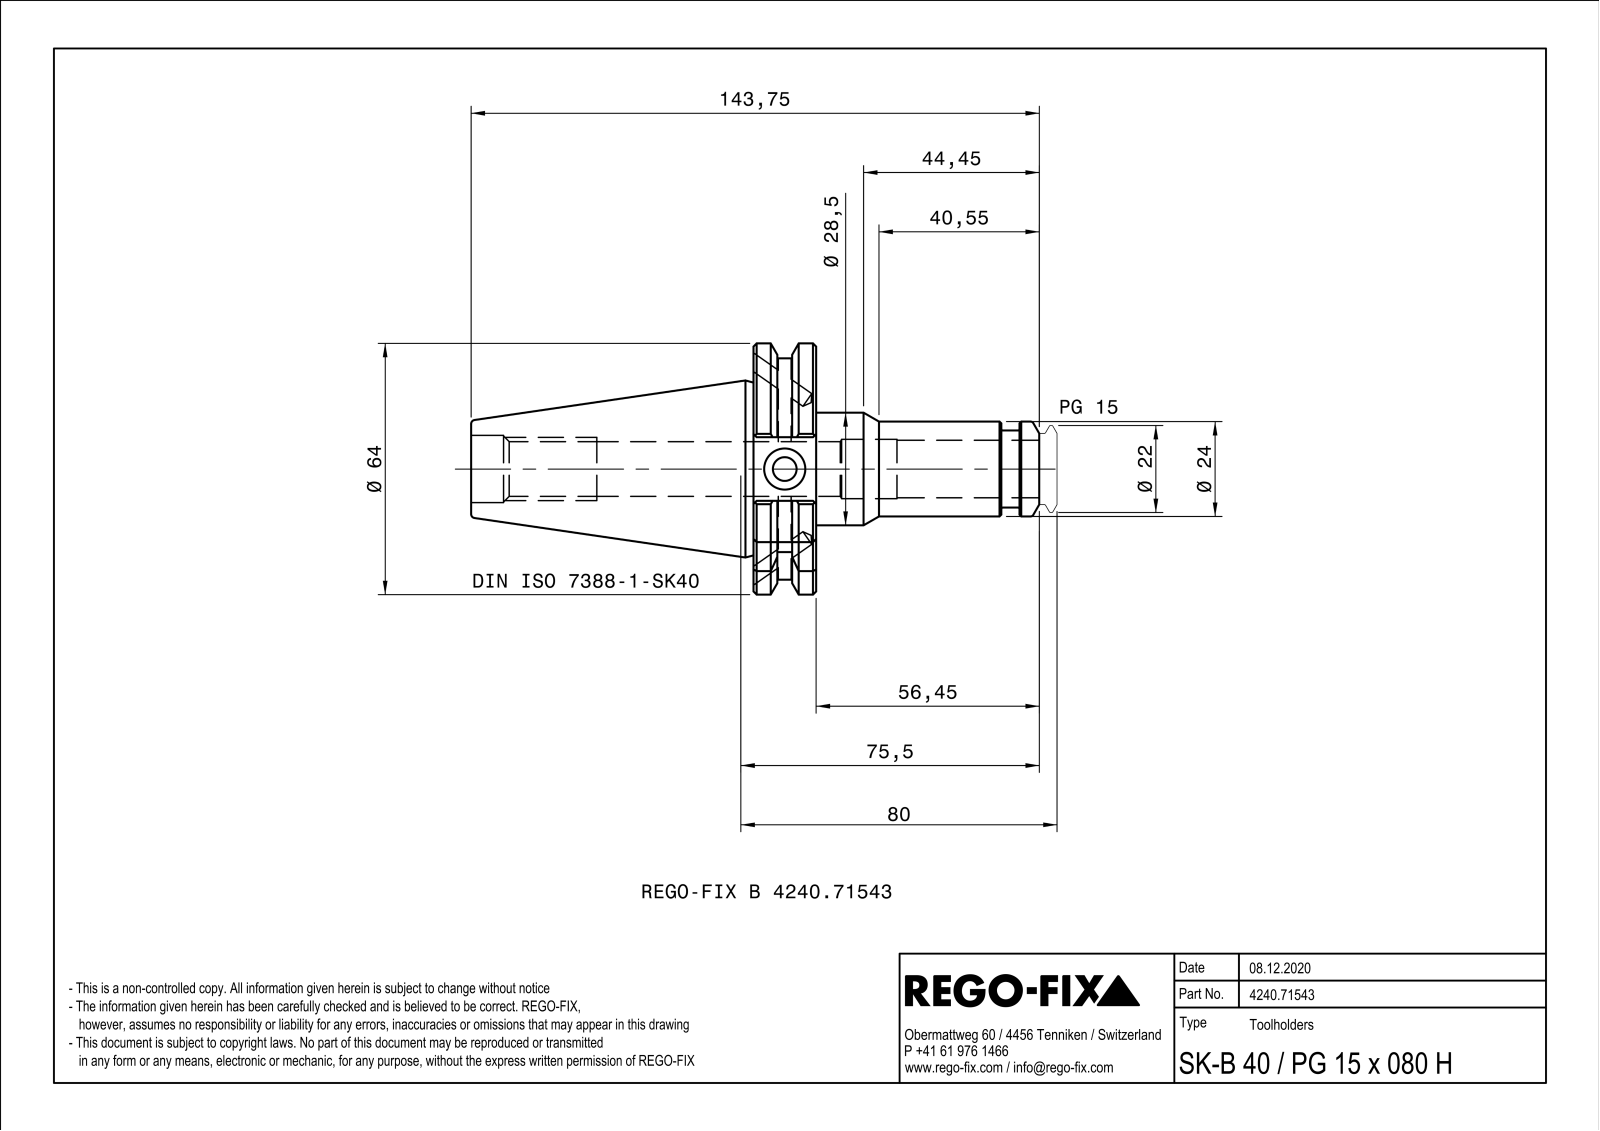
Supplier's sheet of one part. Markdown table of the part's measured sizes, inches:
| quantity | value |
| --- | --- |
| part name | NOCUT |
| STEP written by | SIEMENS PLM Software Solid Edge ST10 (AUTOMOTIVE_DESIGN) |
| units | inches |
| bodies | 1 solid, 139 faces (43 planar, 44 cylindrical, 52 other) |
| overall size | 5.659 × 2.502 × 2.402 |
| volume | 7.096 in³ |
| surface area | 42.86 in² |
| round holes (diameter × count) | 0.138 × 5, 0.236 × 1, 0.394 × 1, 0.545 × 1, 0.591 × 1, 0.669 × 1 |
| round bosses / shafts (diameter × count) | 1.122 × 1, 0.945 × 1, 0.768 × 1 |
| partial cylindrical surfaces (radius × count) | 0.02 × 13, 1.102 × 1, 1.251 × 1 |
| main face-to-face distances | 0.624, 1.862, 0.634, 3.437, 2.813, 1.844, 2.469, 5.281, 0.181, 2.026 |
